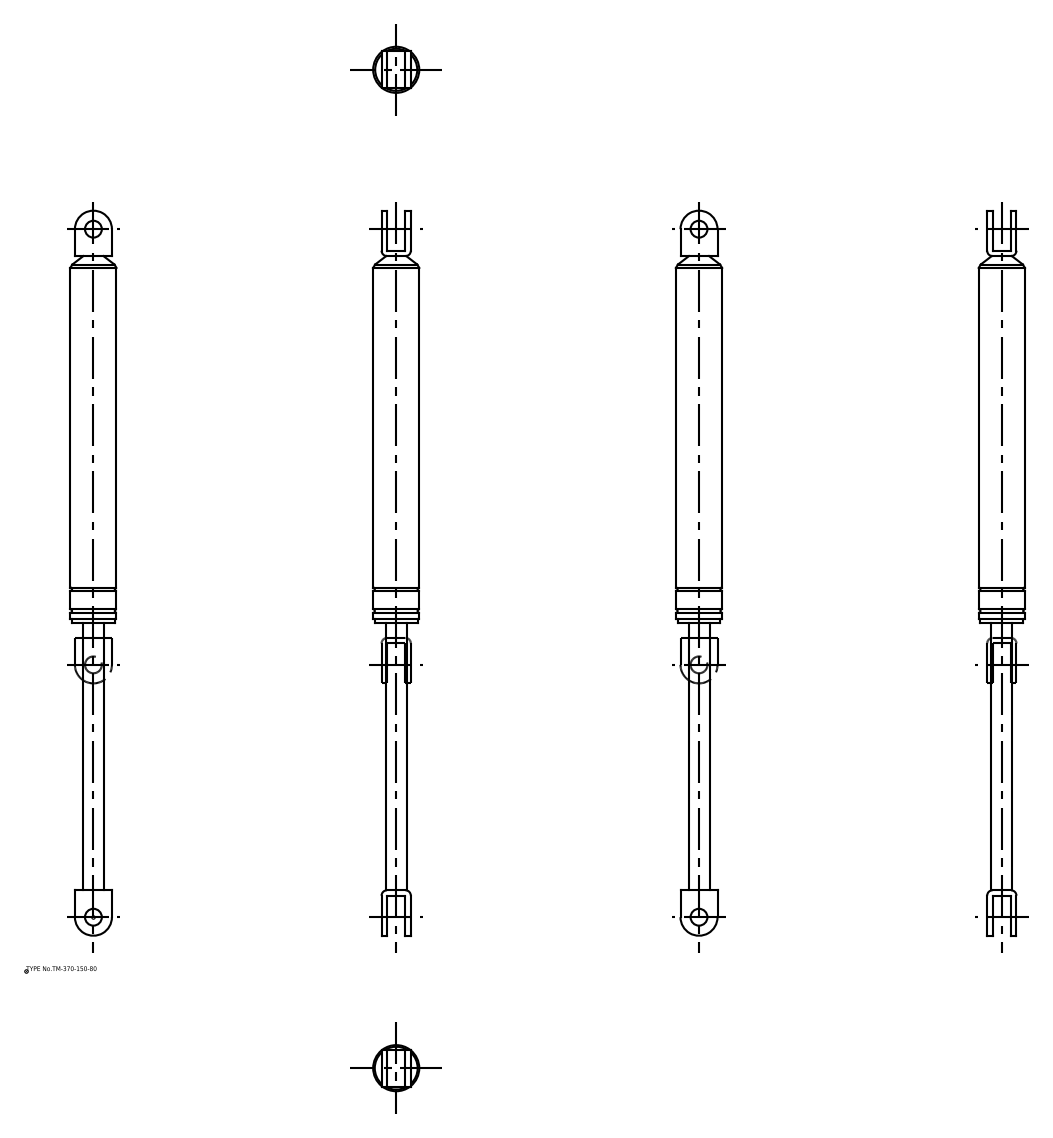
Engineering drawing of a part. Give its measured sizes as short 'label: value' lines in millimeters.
name: TM_370_150_80; TM_370_150_80_div
written by: spGate 16.7.1 (AUTOMOTIVE_DESIGN)
unit: mm
bodies: 2 solids, 64 faces (22 planar, 32 cylindrical, 10 other)
size: 431 × 28.2 × 28.2
volume: 153 749 mm³; area: 31 790 mm²
holes: 2× ⌀10
bosses: 1× ⌀28.2, 1× ⌀27.4, 1× ⌀25.5, 1× ⌀12.5
rounds: 4× R3.2, 2× R11
face distances: 3.2, 14.2, 17.4, 11, 22, 380.2, 162.2, 383.4, 221.2, 218
hole spacings: 409
